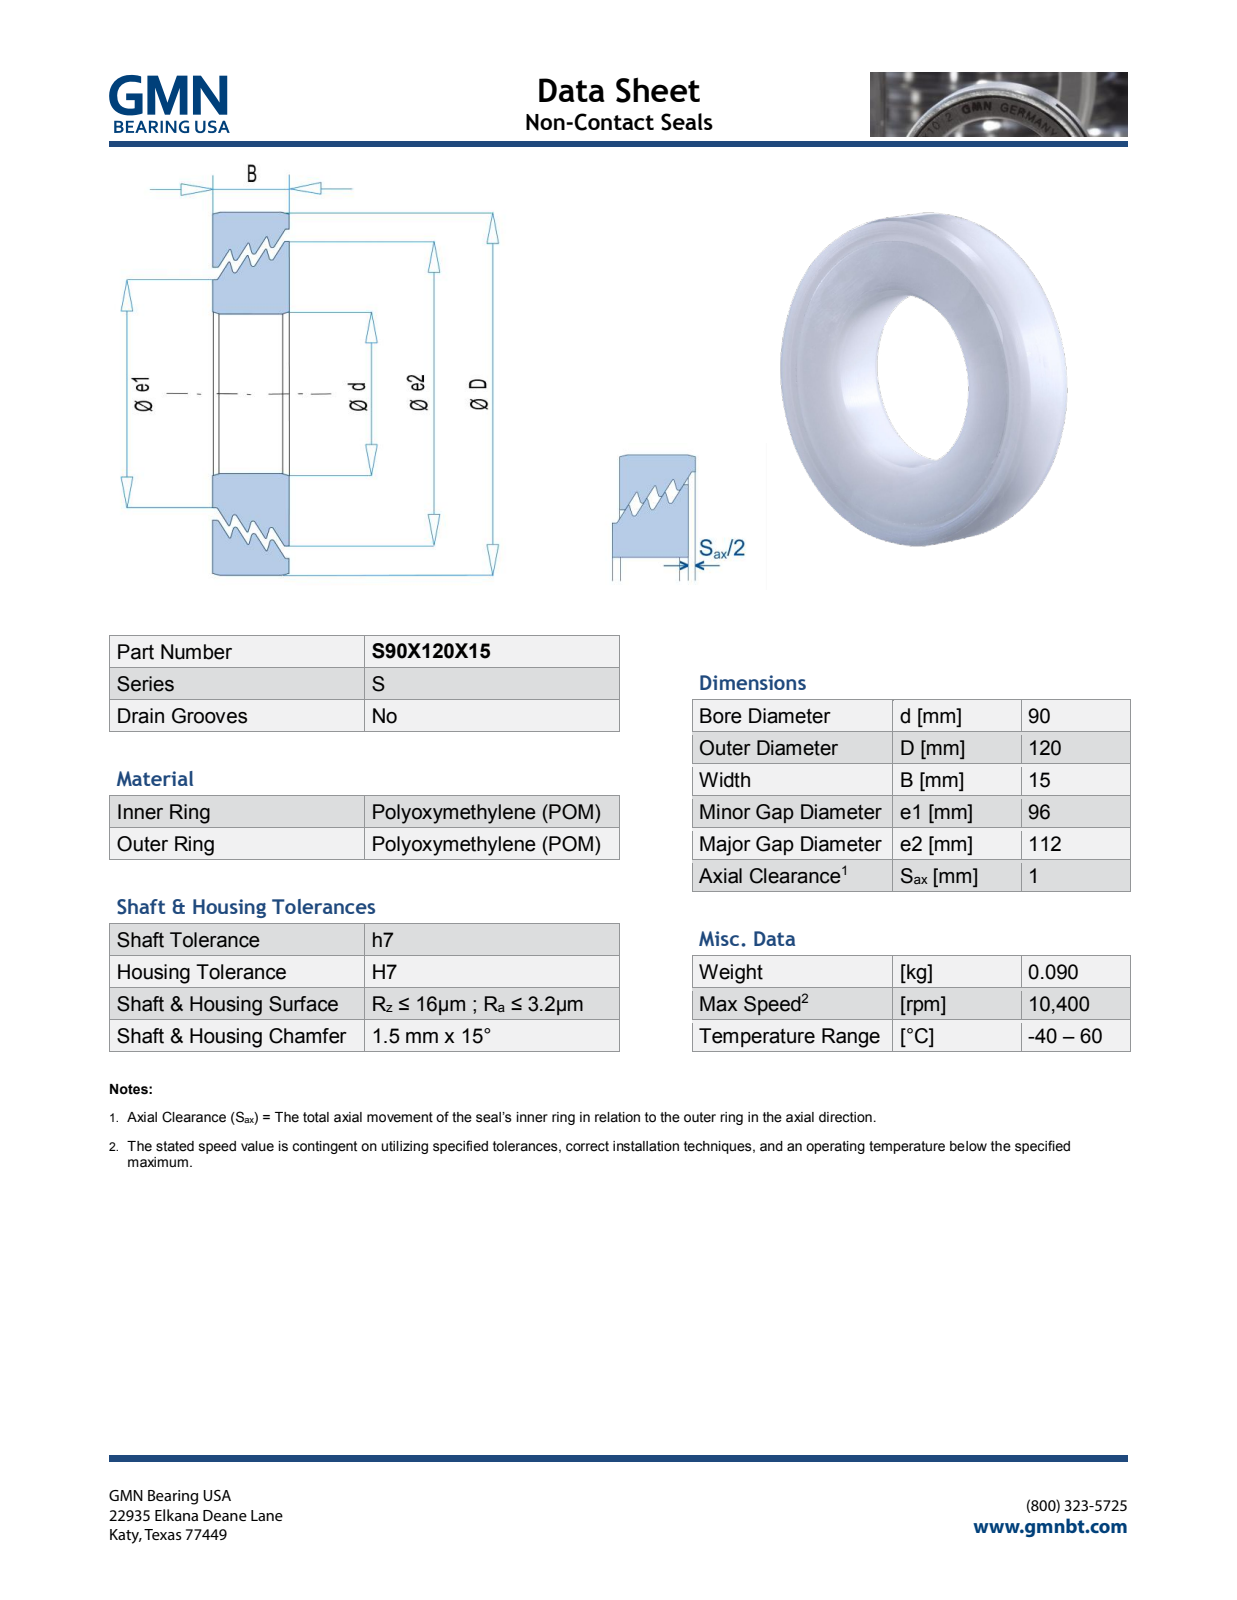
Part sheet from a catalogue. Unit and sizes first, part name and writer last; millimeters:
Units: millimetres
Overall size (bounding box): 120 × 120 × 15.07
Round holes (diameter × count): ⌀90 ×1, ⌀97.63 ×1, ⌀113.63 ×1
Round bosses / shafts (diameter × count): ⌀120 ×1, ⌀112 ×1, ⌀96 ×1
Main face-to-face distances: 15, 15.07, 2.15, 1.88, 2.14, 1.52, 1.87, 1.61, 1.79, 1.6
Volume: 68 669 mm³ · Surface area: 36 670 mm²
Bodies: 2 solids, 695 faces (599 planar, 12 cylindrical, 84 other)
Part name (STEP PRODUCT): S90X120X15_PRT
STEP written by: PRO/ENGINEER BY PARAMETRIC TECHNOLOGY CORPORATION, 2013150 (AUTOMOTIVE_DESIGN)
